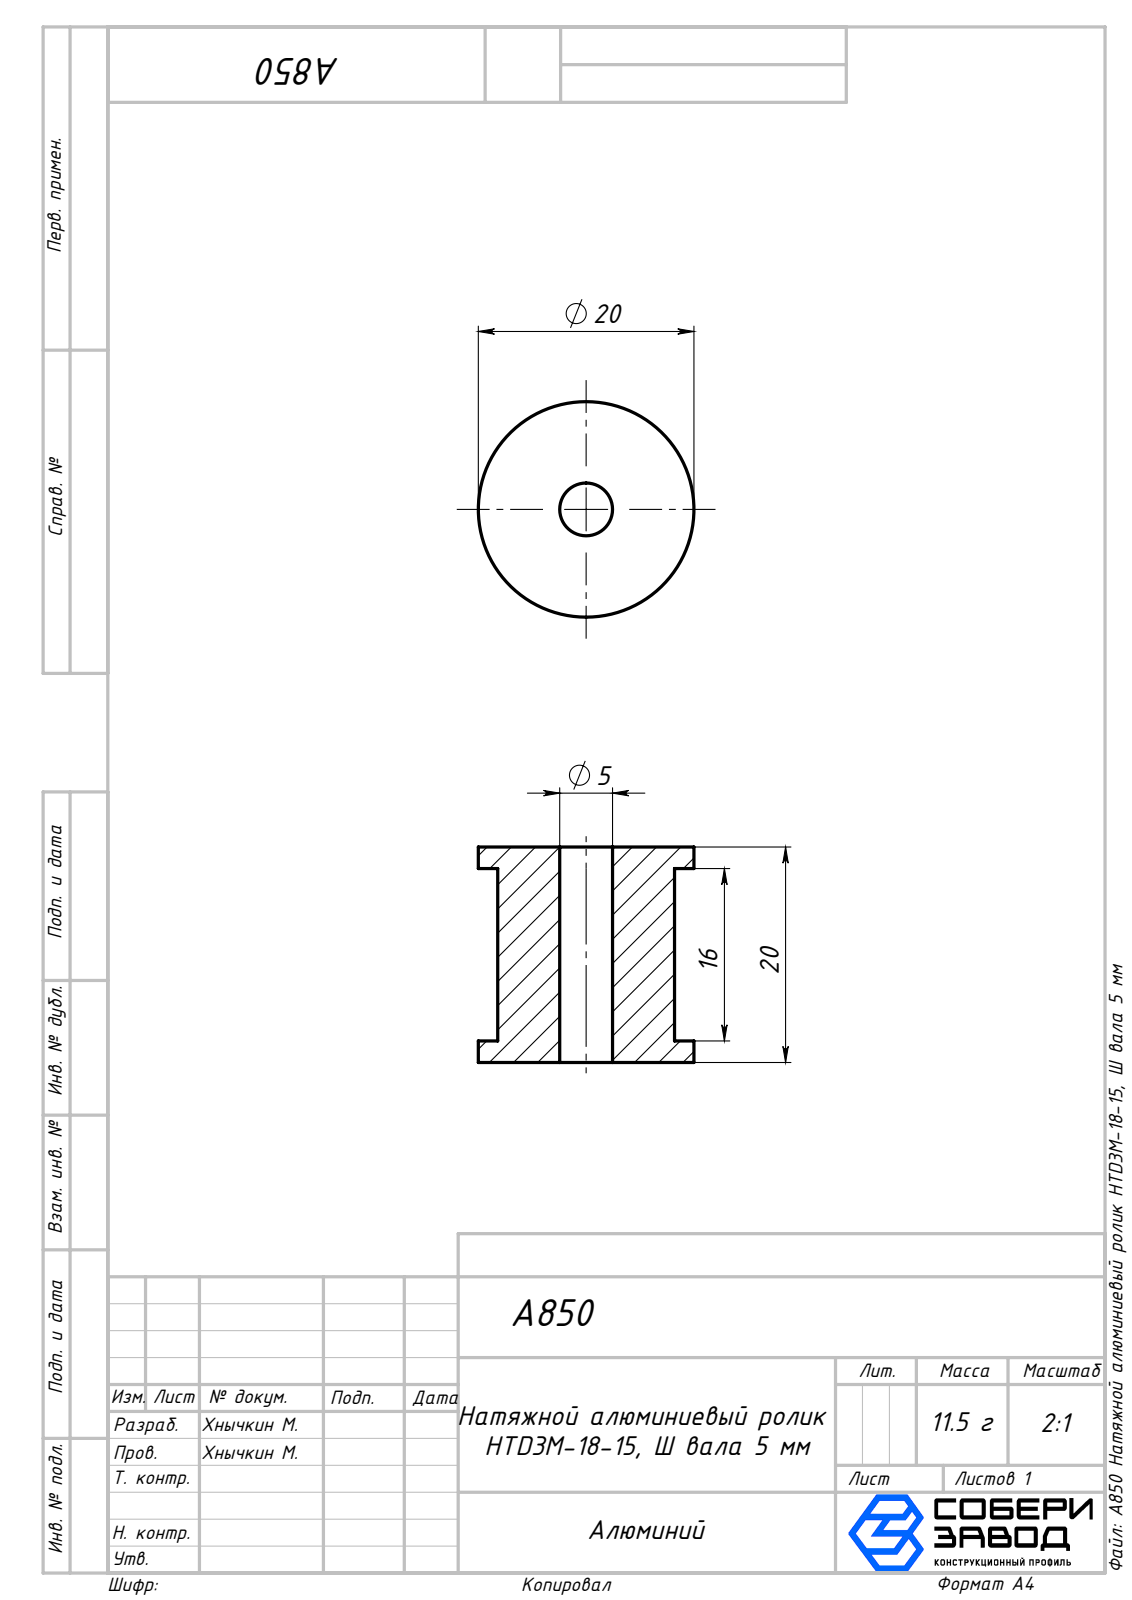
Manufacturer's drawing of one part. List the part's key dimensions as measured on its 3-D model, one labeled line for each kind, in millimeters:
Part name (STEP PRODUCT): A850 Натяжной алюминиевый ролик HTD3M-18-15, Ø вала 5 мм
STEP written by: SolidWorks 2025 (AUTOMOTIVE_DESIGN)
Units: millimetres
Bodies: 1 solid, 12 faces (4 planar, 8 cylindrical, 0 other)
Overall size (bounding box): 20 × 20 × 20
Volume: 4 259 mm³ · Surface area: 2 180 mm²
Round holes (diameter × count): ⌀4.9 ×1
Round bosses / shafts (diameter × count): ⌀20 ×1, ⌀16.4 ×1
Main face-to-face distances: 20, 2, 18, 16
